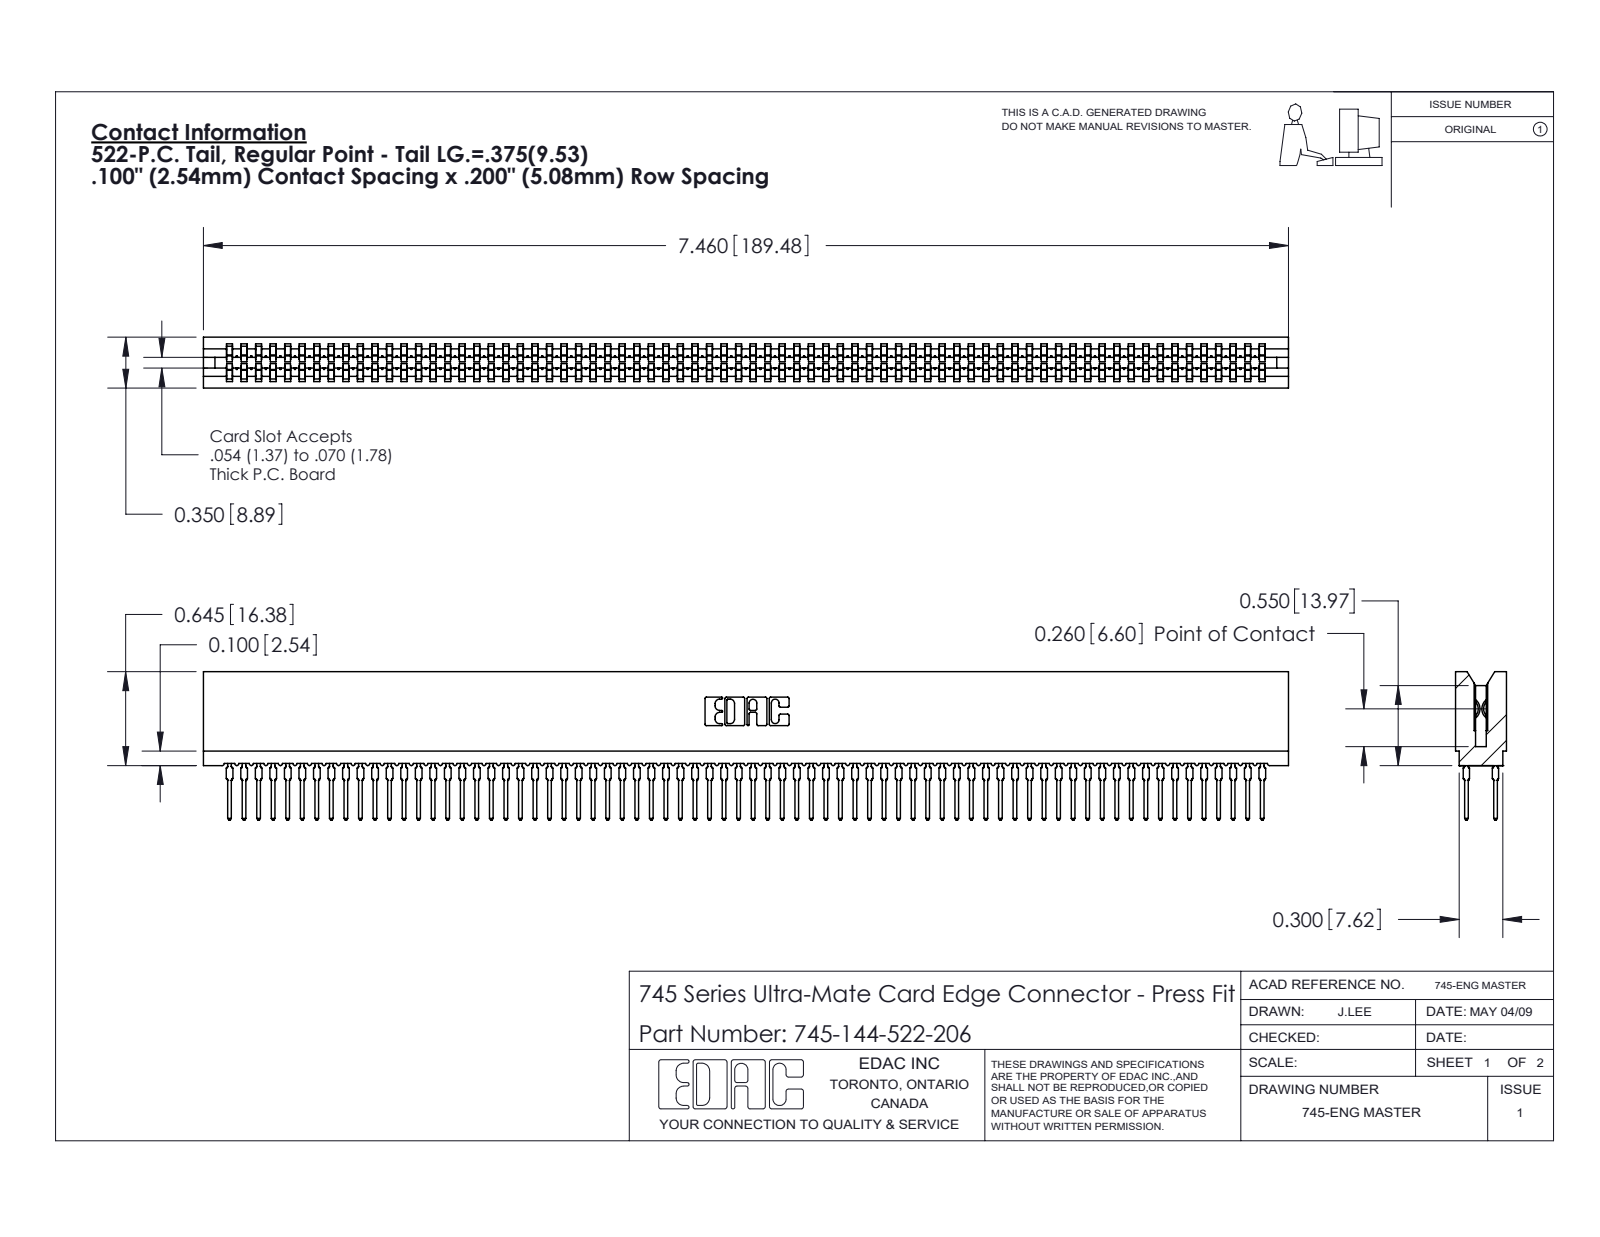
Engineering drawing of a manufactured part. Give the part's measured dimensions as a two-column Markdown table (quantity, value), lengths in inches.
| quantity | value |
| --- | --- |
| part name | 745-292-001_522; 745 Part_Insulator Option - 06; 745-144-522-206 |
| STEP written by | SolidWorks 2020 (CONFIG_CONTROL_DESIGN) |
| units | inches |
| bodies | 145 solids, 12984 faces (6680 planar, 2560 cylindrical, 3744 other) |
| overall size | 7.46 × 1.021 × 0.35 |
| volume | 1.038 in³ |
| surface area | 55.5 in² |
| partial cylindrical surfaces (radius × count) | 0.021 × 288, 0.015 × 144, 0.01 × 22, 0.005 × 8, 0.011 × 8, 0.007 × 6, 0.031 × 6, 0.026 × 3 |
| main face-to-face distances | 0.35, 0.063, 0.287, 0.045, 0.305, 0.018, 0.243, 0.138, 0.212, 0.093 |
